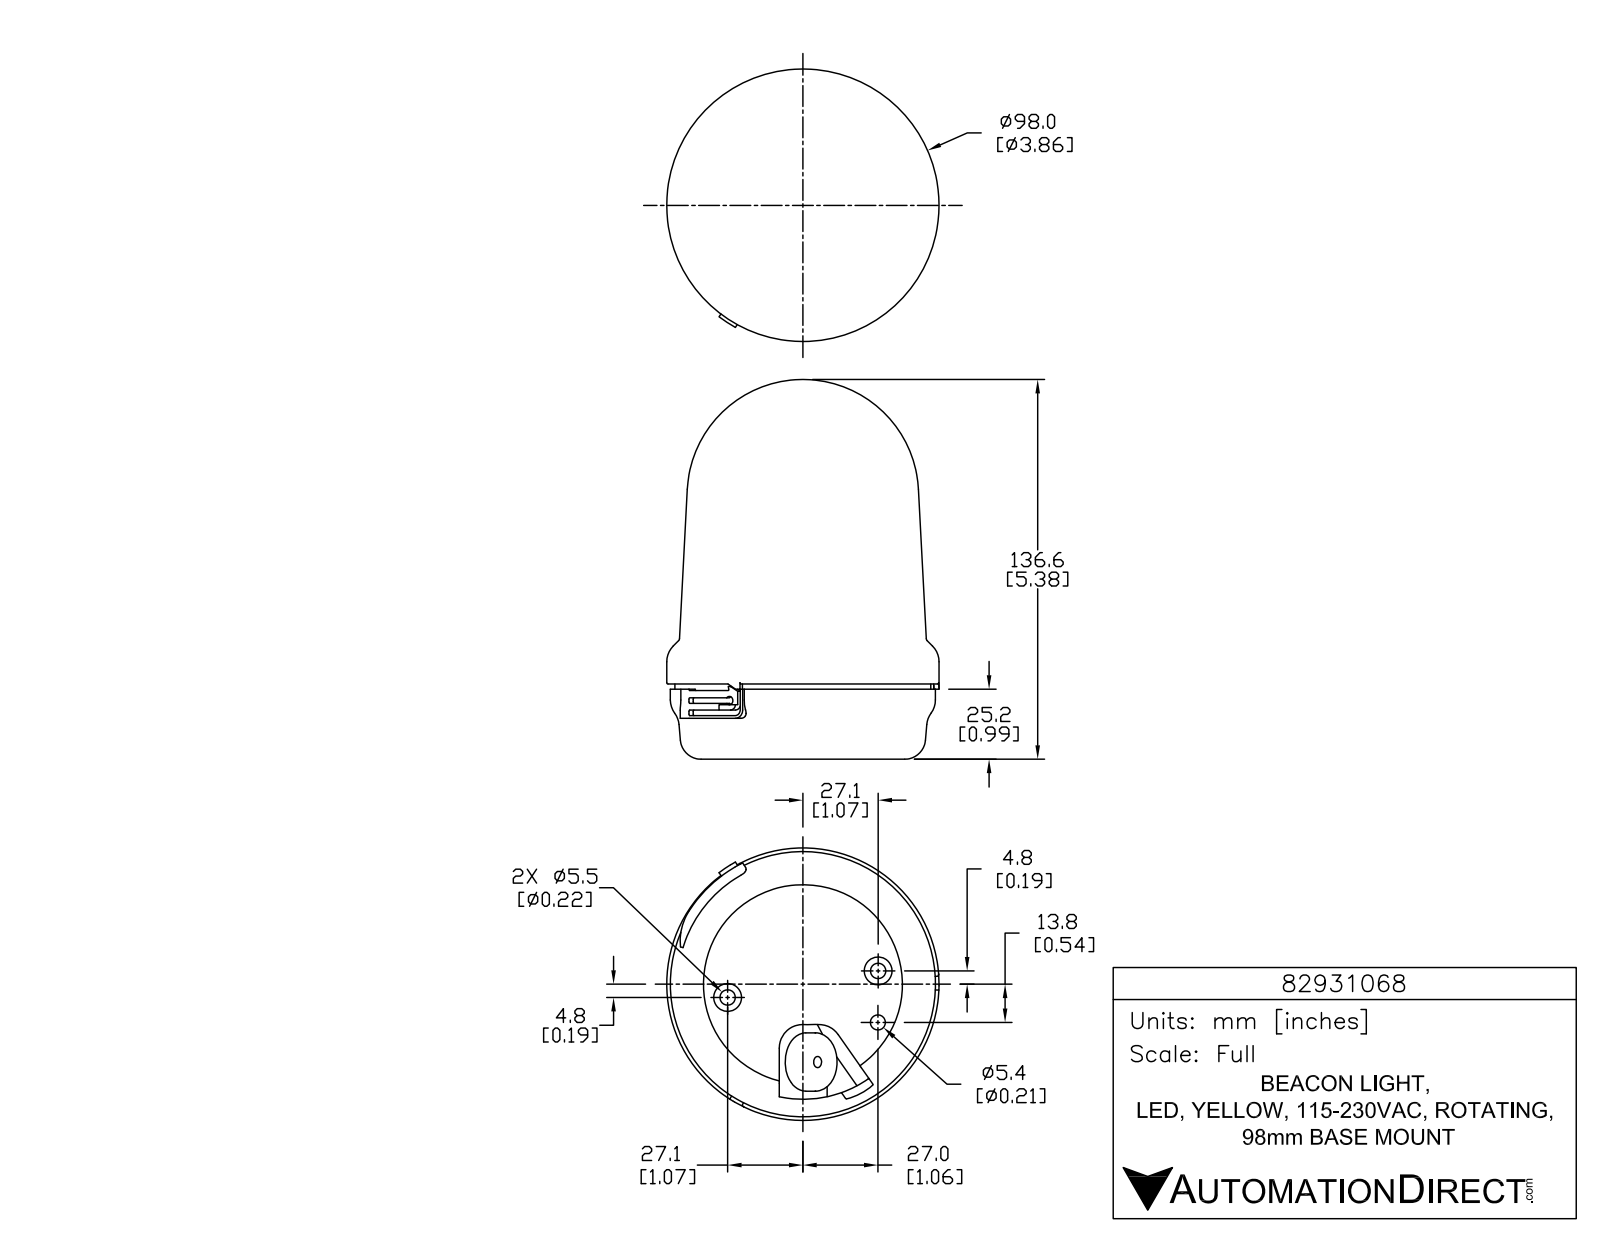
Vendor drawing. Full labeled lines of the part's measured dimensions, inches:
Part name (STEP PRODUCT): 82931068
STEP written by: SolidWorks 2015 (AUTOMOTIVE_DESIGN)
Units: inches
Bodies: 1 solid, 872 faces (566 planar, 204 cylindrical, 102 other)
Overall size (bounding box): 5.378 × 3.858 × 3.858
Volume: 44.69 in³ · Surface area: 73.66 in²
Round holes (diameter × count): ⌀0.059 ×3, ⌀0.217 ×2, ⌀0.157 ×1, ⌀0.213 ×1, ⌀2.819 ×1
Round bosses / shafts (diameter × count): ⌀0.339 ×3, ⌀0.084 ×3, ⌀0.394 ×2, ⌀3.858 ×1, ⌀3.756 ×1, ⌀3.626 ×1, ⌀0.827 ×1
Partial cylindrical surfaces — rounded edges, fillets, slot ends (radius × count): R0.005 ×9, R0.005 ×6, R0.012 ×6, R0.012 ×6, R0.012 ×6, R0.196 ×6, R0.02 ×5, R0.039 ×4
Main face-to-face distances: 1.045, 0.972, 0.073, 0.02, 0.992, 1.065, 0.236, 0.579, 0.559, 0.413
Hole centre spacings: 1.083, 0.73, 1.193, 2.158, 2.165
